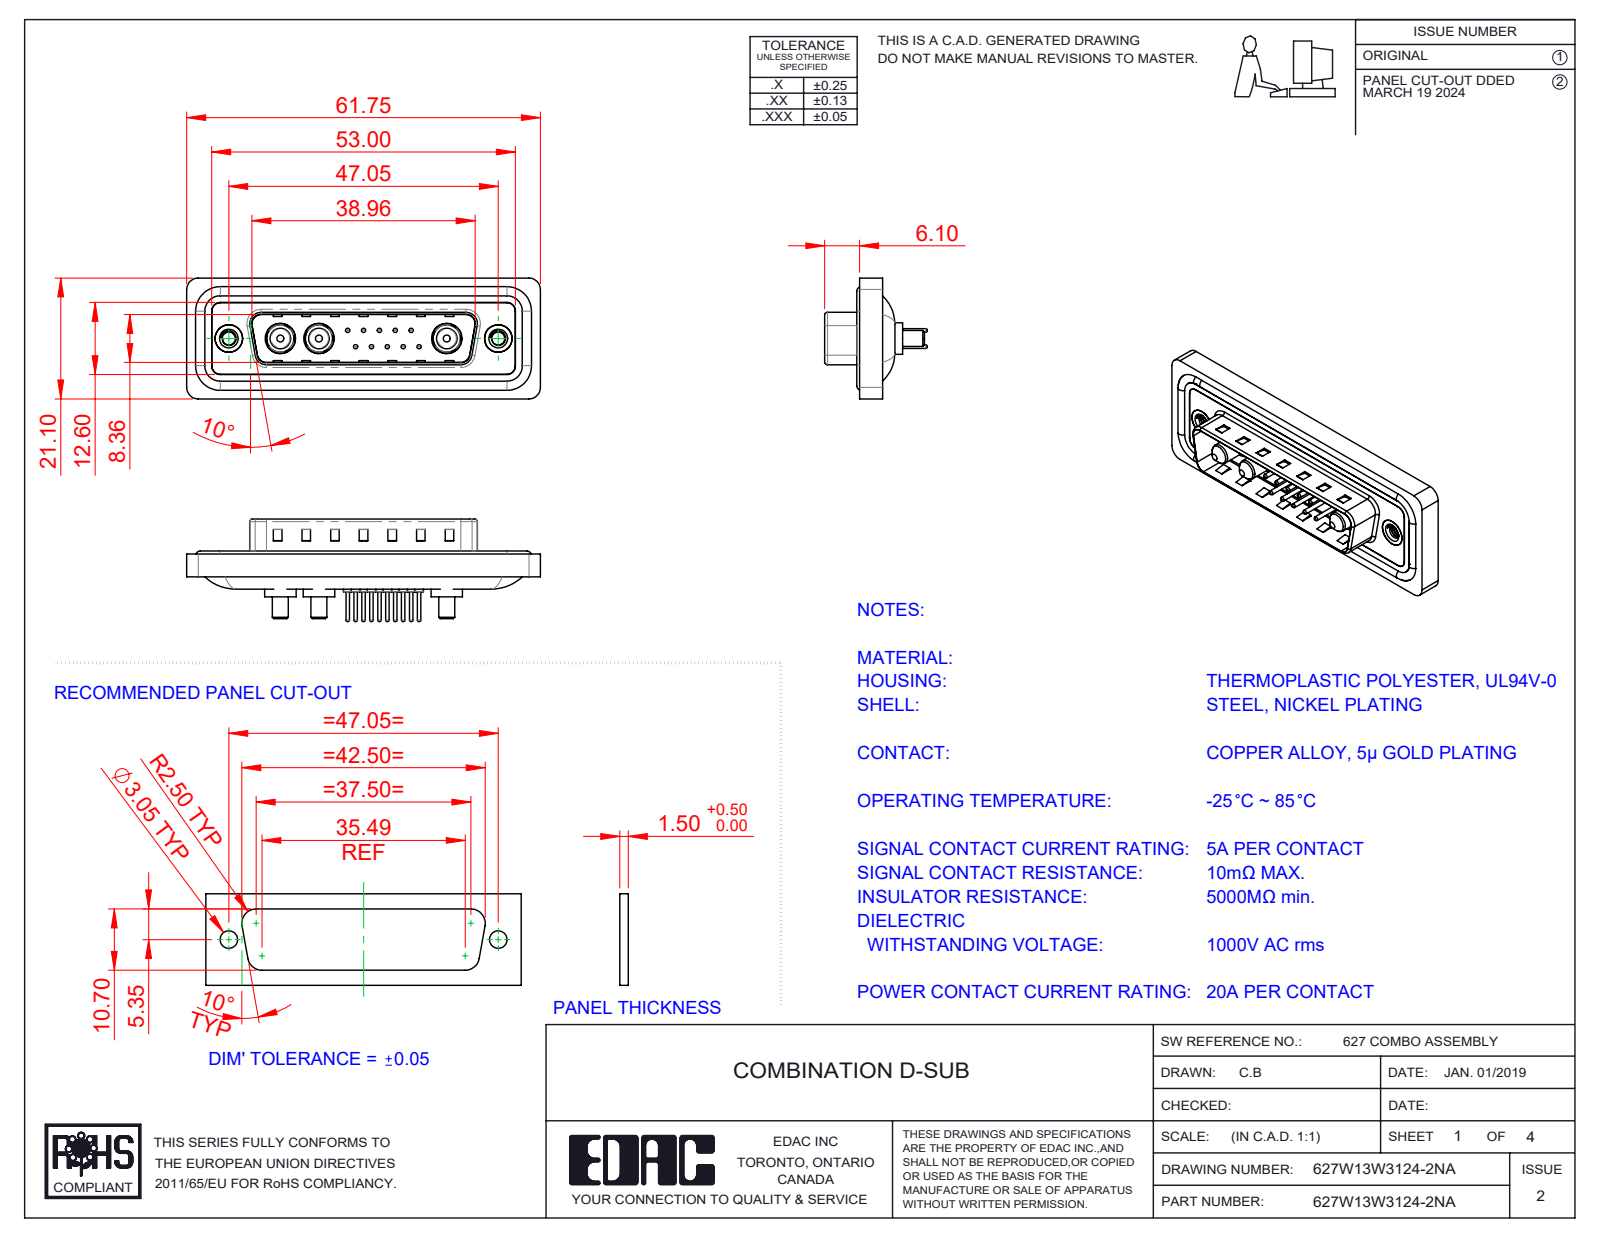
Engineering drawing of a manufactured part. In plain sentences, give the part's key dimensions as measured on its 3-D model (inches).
The part is named "627Combo Threaded Rivet_A; 627Combo Contact Row 1_24; 627W13W3124-2NA; 627Combo Waterproof Housing_25 Contacts (+5 more)". Its 3-D file was written by "SolidWorks 2023 (CONFIG_CONTROL_DESIGN)". It is 23 solids with 968 faces: 309 planar, 387 cylindrical and 272 other. Overall it measures 2.431 by 0.831 by 0.705 inches. Its volume is 0.448 cubic inches and its surface area 18.4 square inches. Round holes: 10 of diameter 0.03, 10 of diameter 0.063, 10 of diameter 0.079, 3 of diameter 0.191, 3 of diameter 0.209, 2 of diameter 0.089, 2 of diameter 0.157, 2 of diameter 0.189, 2 of diameter 0.197. Round bosses or shafts: 10 of diameter 0.059, 10 of diameter 0.024, 4 of diameter 0.063, 3 of diameter 0.217, 3 of diameter 0.205, 3 of diameter 0.187, 3 of diameter 0.148, 3 of diameter 0.142. Partial cylindrical surfaces (rounded edges, fillets, slot ends): 22 of radius 0.059, 18 of radius 0.079, 8 of radius 0.02, 8 of radius 0.063, 4 of radius 0.01, 4 of radius 0.024, 4 of radius 0.026, 4 of radius 0.035. The main face-to-face distances are 0.016, 0.059, 0.043, 0.063, 0.02, 0.122, 0.114, 0.032, 0.377, 0.161. The hole center spacings are 0.124, 0.109, 0.198, 0.218, 0.295, 0.198, 0.327, 0.398.
